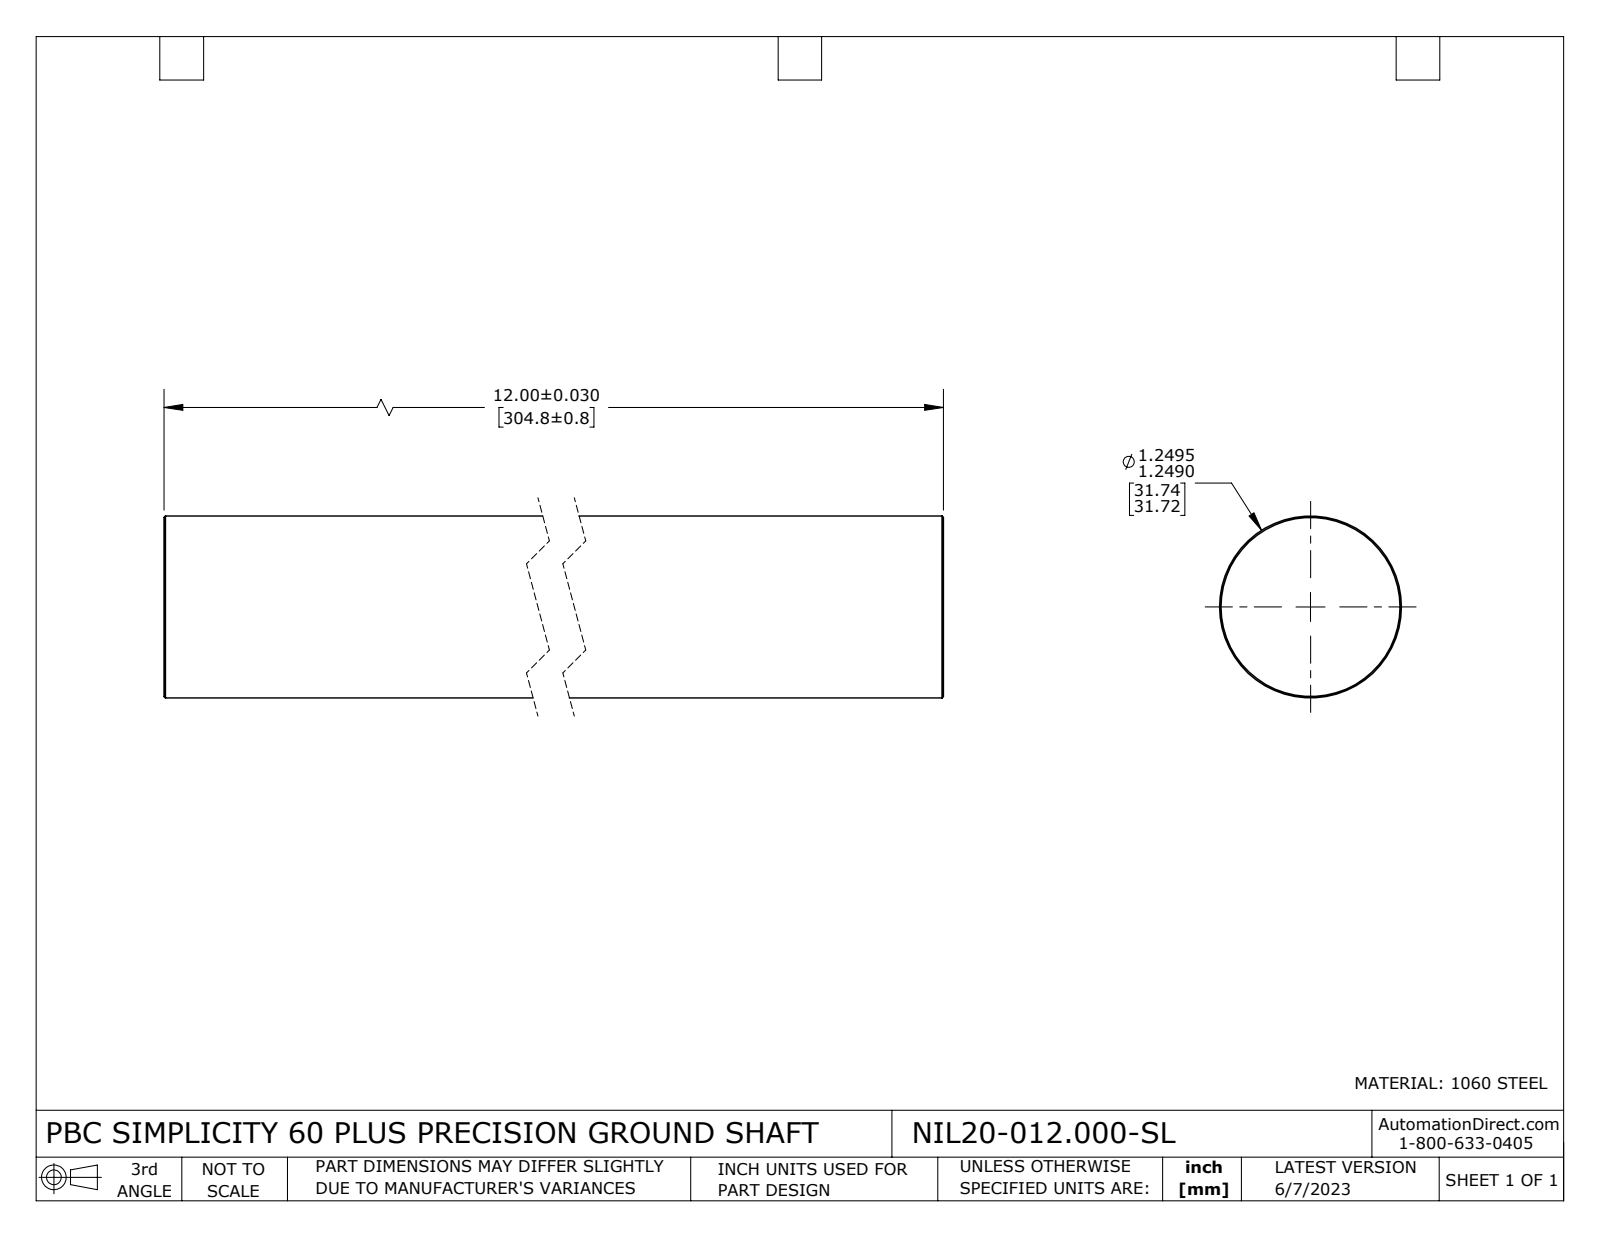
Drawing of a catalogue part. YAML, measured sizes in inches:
part_name: "NIL20-012.000-SL"
step_written_by: "SolidWorks 2021 (CONFIG_CONTROL_DESIGN)"
units: inches
bodies: {solids: 1, faces: 8, planar: 2, cylindrical: 2, other: 4}
overall_size: [12, 1.25, 1.25]
volume: 14.73
surface_area: 49.53
round_bosses_or_shafts:
  - {diameter: 1.25, count: 1}
face_to_face_distances: [12]
